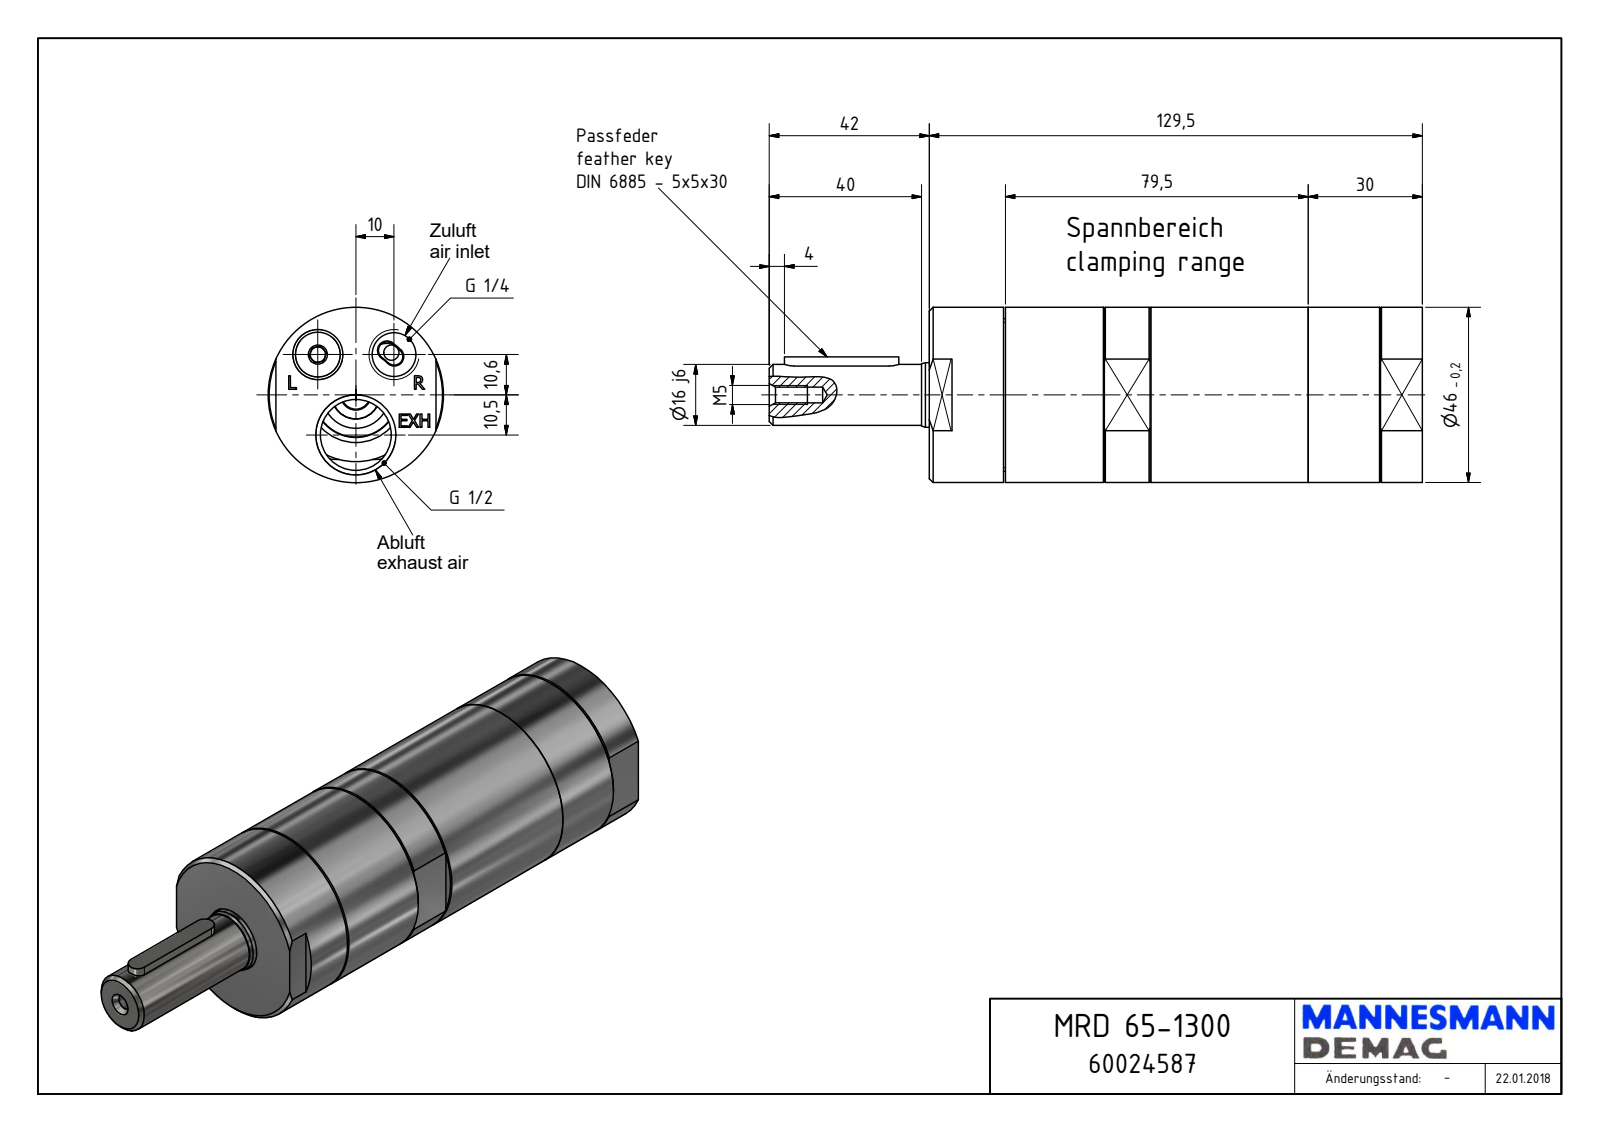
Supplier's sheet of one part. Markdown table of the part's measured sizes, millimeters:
| quantity | value |
| --- | --- |
| part name | MRD 65-1300_60024587 |
| STEP written by | Autodesk Inventor 2018 (AUTOMOTIVE_DESIGN) |
| units | millimeters |
| bodies | 1 solid, 175 faces (106 planar, 37 cylindrical, 32 other) |
| overall size | 171.5 × 46 × 46 |
| volume | 214 911 mm³ |
| surface area | 28 258 mm² |
| round holes (diameter × count) | 11.45 × 2, 2.8 × 1, 4 × 1, 4.13 × 1, 17.5 × 1, 18.63 × 1 |
| round bosses / shafts (diameter × count) | 46 × 1, 40 × 1, 16.95 × 1, 16 × 1 |
| partial cylindrical surfaces (radius × count) | 2.5 × 6, 5 × 2, 7 × 1, 9 × 1, 11.75 × 1, 16.75 × 1, 19 × 1 |
| main face-to-face distances | 129.5, 13.32, 116.18, 42, 0.5, 20, 96.18, 109.5, 19.5, 96.68 |
| hole center spacings | 10.73, 14.57, 23.35, 10.5, 14.5, 20, 25 |
